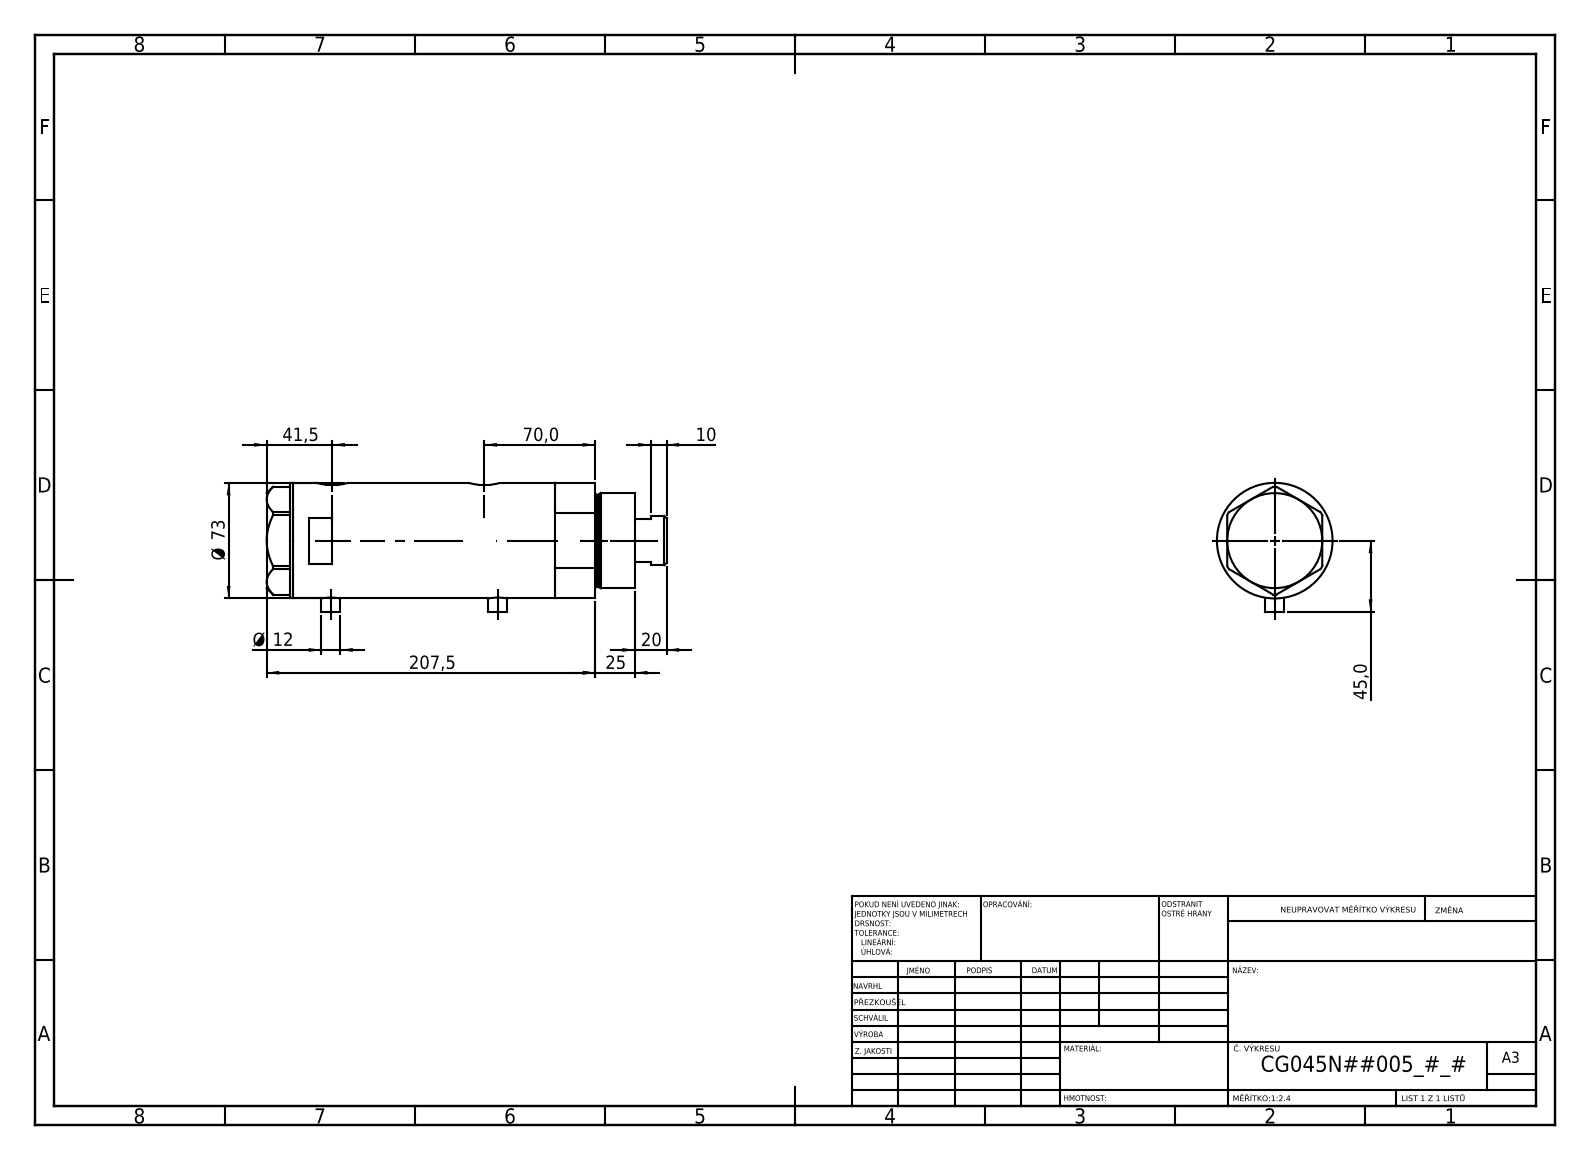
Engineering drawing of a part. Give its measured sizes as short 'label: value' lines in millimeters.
name: V270CG_BACK; V270CG_MIDDLE; V270CG_FRONT; V270CG_VC
written by: SolidWorks 2019 (CONFIG_CONTROL_DESIGN)
unit: mm
bodies: 4 solids, 120 faces (49 planar, 51 cylindrical, 20 other)
size: 252.5 × 81.5 × 73
volume: 921 523 mm³; area: 150 789 mm²
holes: 2× ⌀12.5, 2× ⌀13.16, 1× ⌀10.5, 1× ⌀32, 1× ⌀33.5, 1× ⌀45, 1× ⌀48, 1× ⌀64
bosses: 2× ⌀12, 1× ⌀73, 1× ⌀60, 1× ⌀58, 1× ⌀31
rounds: 2× R10
face distances: 95, 121, 26, 16.5, 42.5, 137.5, 2, 216, 232.5, 190
hole spacings: 1, 8.5, 96, 97, 104.5, 105.5
